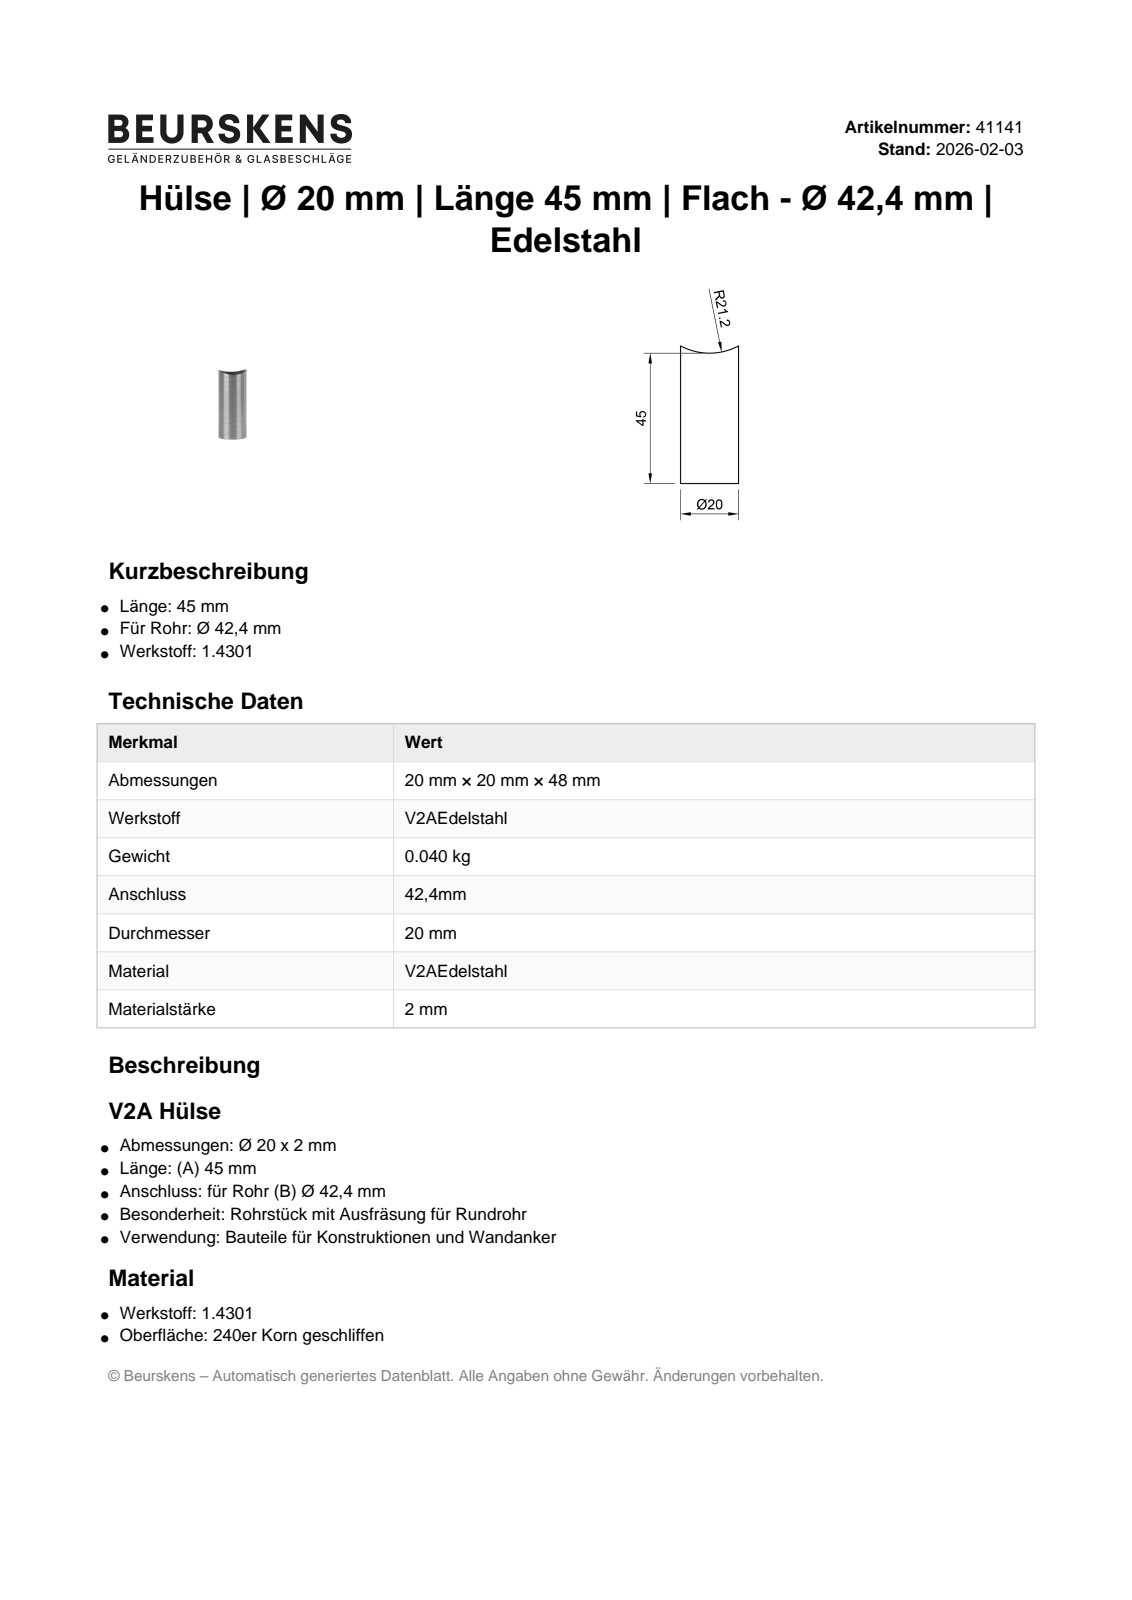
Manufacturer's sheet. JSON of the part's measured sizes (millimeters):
{"part_name": "41141", "step_written_by": "Autodesk Inventor 2022 (AUTOMOTIVE_DESIGN)", "units": "millimeters", "bodies": {"solids": 1, "faces": 4, "planar": 1, "cylindrical": 3, "other": 0}, "overall_size": [47.51, 20, 20], "volume_mm3": 2752, "surface_area_mm2": 5628, "round_holes": [[18, 1]], "round_bosses_or_shafts": [[20, 1]], "partial_cylinders_radius": [[21.2, 1]]}
